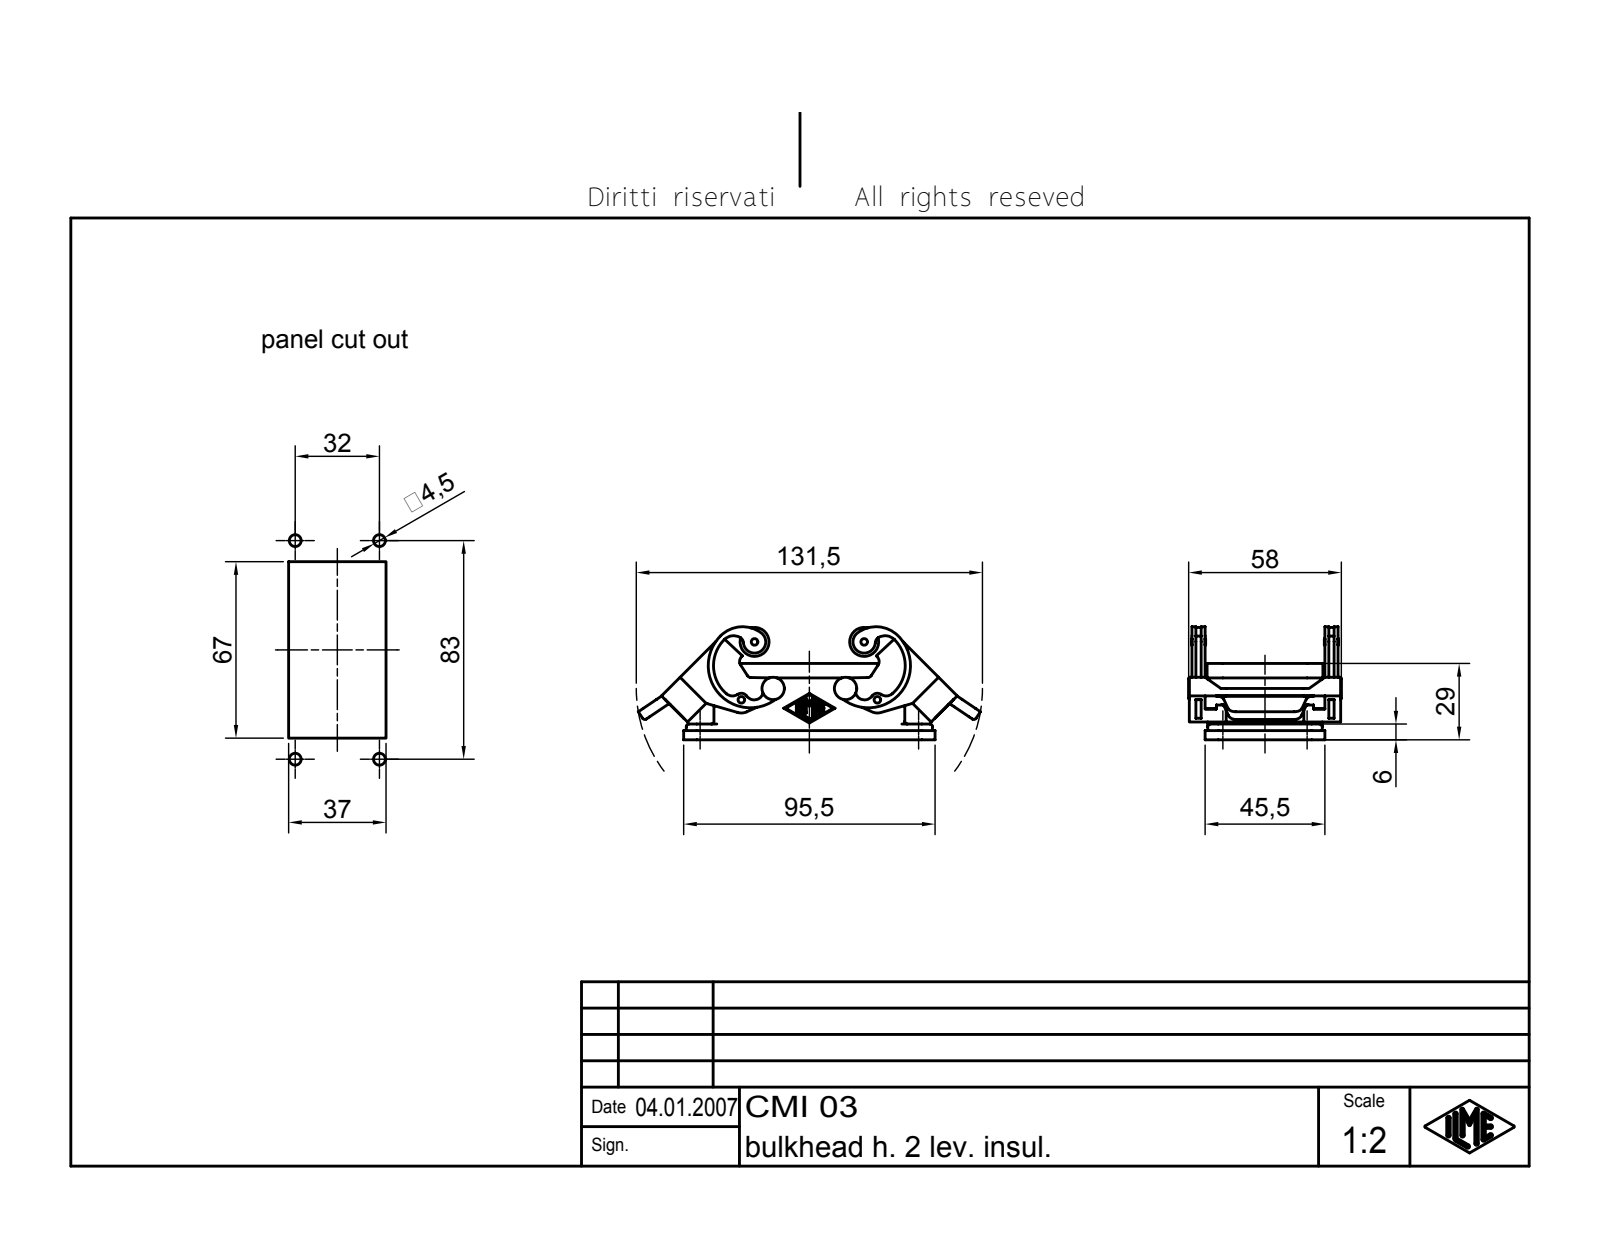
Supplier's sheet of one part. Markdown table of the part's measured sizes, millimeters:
| quantity | value |
| --- | --- |
| part name | CMI 03 |
| STEP written by | Autodesk Inventor 7 (AUTOMOTIVE_DESIGN) |
| units | millimeters |
| bodies | 1 solid, 749 faces (201 planar, 220 cylindrical, 328 other) |
| overall size | 129.99 × 58 × 42.94 |
| volume | 49 103 mm³ |
| surface area | 33 892 mm² |
| round holes (diameter × count) | 2 × 4, 4.5 × 4, 4.6 × 4, 2.5 × 2 |
| round bosses / shafts (diameter × count) | 11 × 2, 5 × 2, 3 × 2 |
| partial cylindrical surfaces (radius × count) | 0.38 × 14, 1 × 14, 3 × 12, 2.5 × 10, 3.5 × 8, 5 × 8, 6 × 8, 4 × 6 |
| main face-to-face distances | 4, 3, 40.5, 1, 3.5, 50.5, 2.5, 0.75, 6, 1.5 |
| hole center spacings | 22.56, 32, 51.58, 83, 88.96, 41.64, 51.68 |
